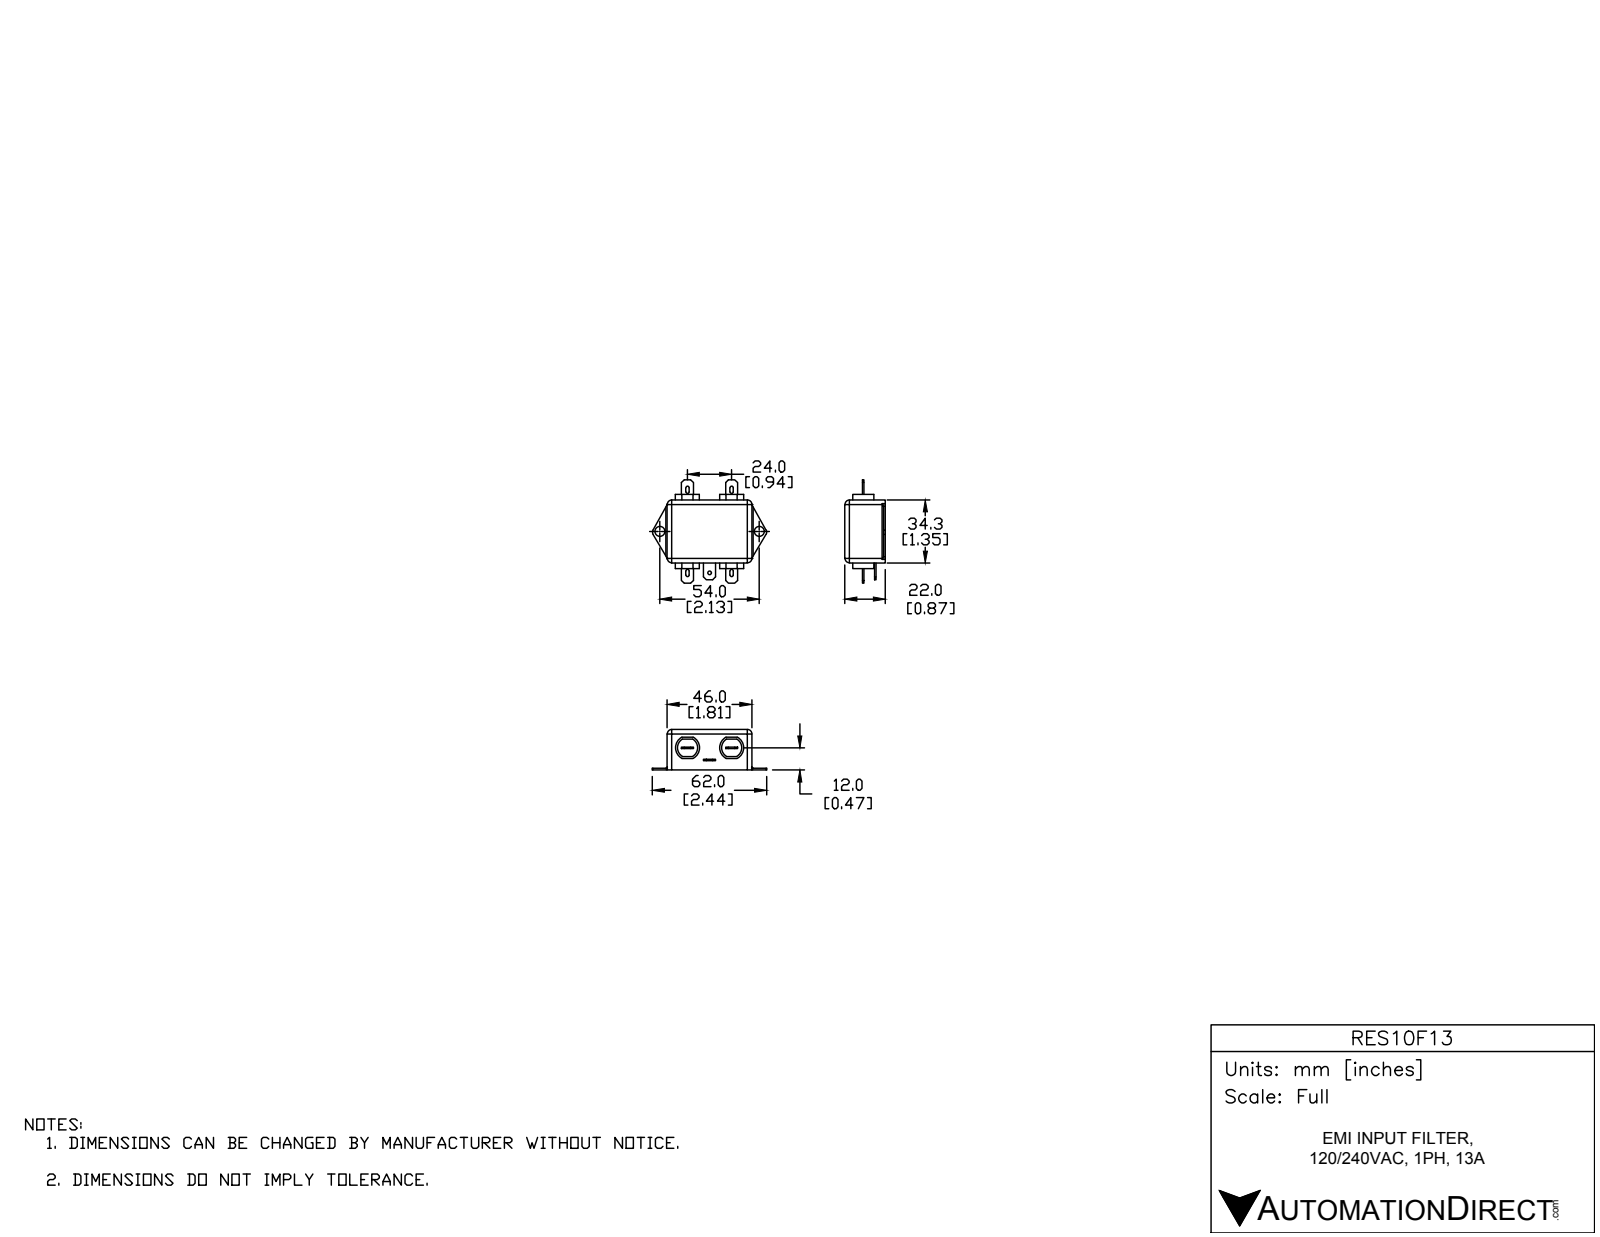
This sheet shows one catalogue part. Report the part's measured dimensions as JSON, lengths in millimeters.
{"part_name": "RES10F13", "step_written_by": "SolidWorks 2015 (AUTOMOTIVE_DESIGN)", "units": "millimeters", "bodies": {"solids": 1, "faces": 137, "planar": 79, "cylindrical": 54, "other": 4}, "overall_size": [61.3, 56.1, 22], "volume_mm3": 35744, "surface_area_mm2": 8153, "round_holes": [[5.3, 2], [2, 1]], "partial_cylinders_radius": [[2.5, 10], [0.9, 8], [0.75, 2], [5.5, 2], [6.5, 2]], "face_to_face_distances": [22, 34.3, 46, 1.4, 35.7, 0.8, 1, 11.6, 12.4, 10.4], "hole_center_spacings": [35.11, 54]}
